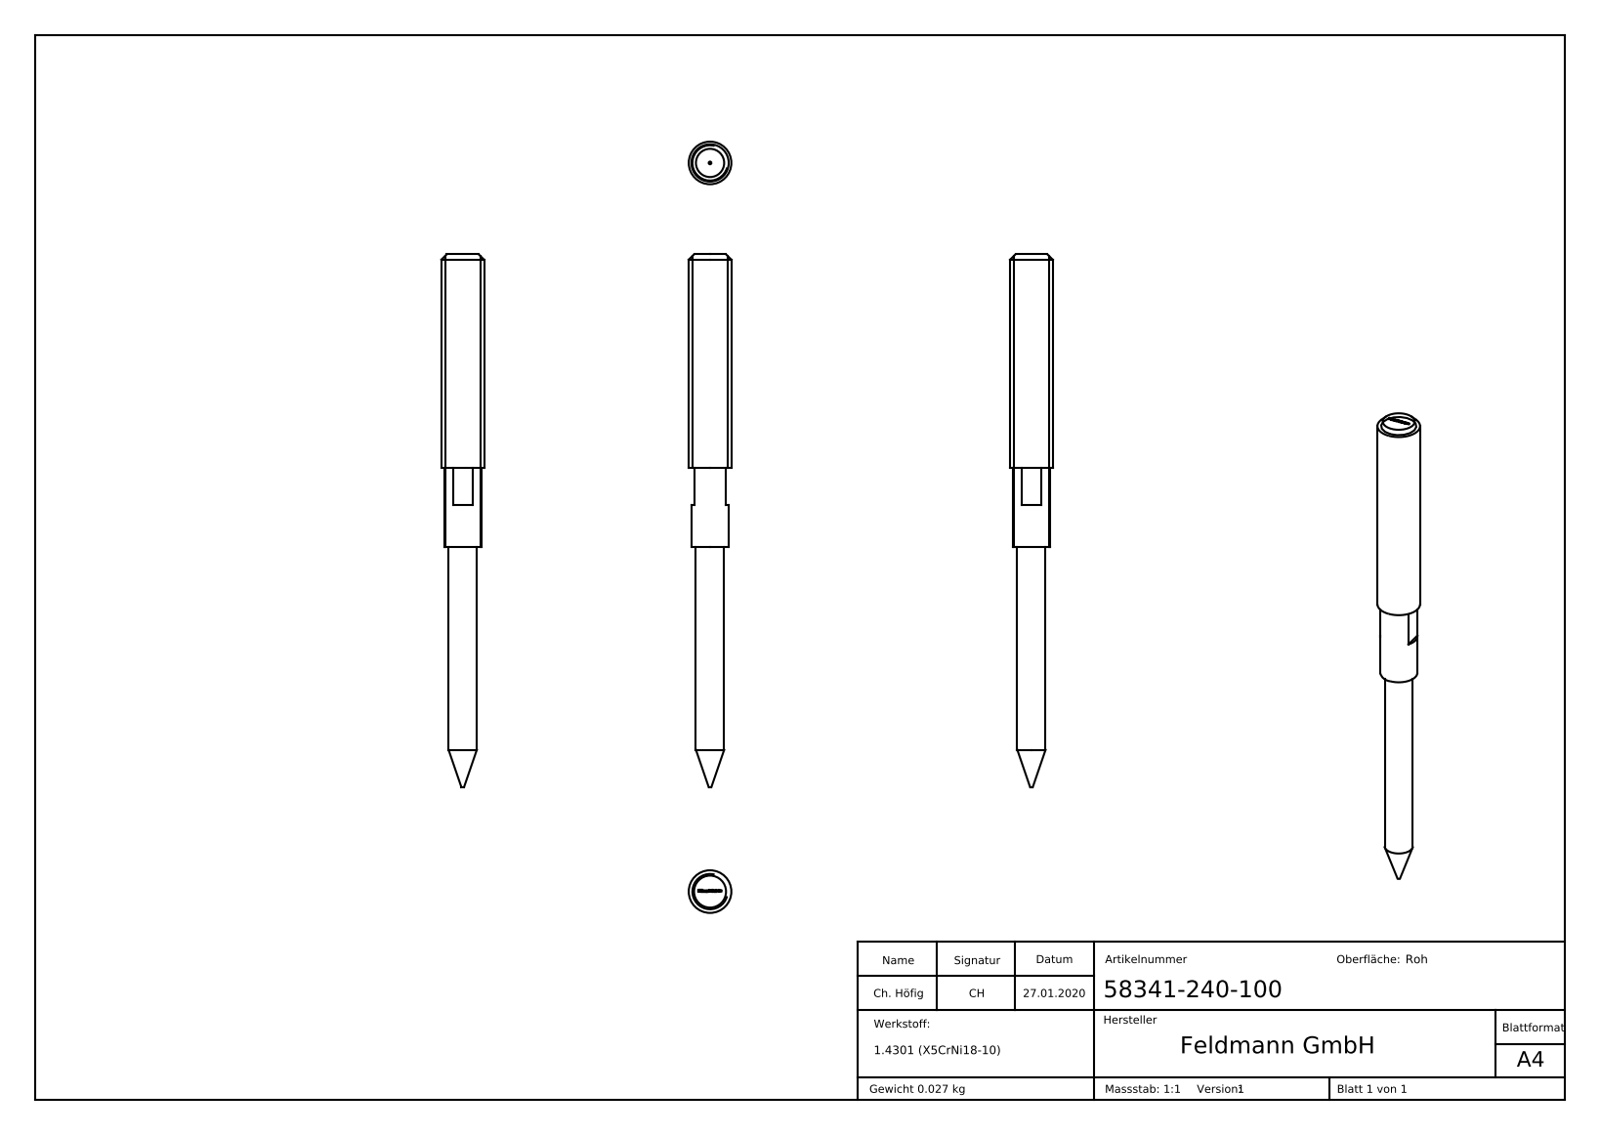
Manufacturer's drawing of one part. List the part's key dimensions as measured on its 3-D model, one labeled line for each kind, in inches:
Part name (STEP PRODUCT): 58341-240-100
STEP written by: SolidWorks 2015 (CONFIG_CONTROL_DESIGN)
Units: inches
Bodies: 1 solid, 269 faces (136 planar, 3 cylindrical, 130 other)
Overall size (bounding box): 3.937 × 0.315 × 0.315
Volume: 0.211 in³ · Surface area: 3.258 in²
Round bosses / shafts (diameter × count): ⌀0.315 ×1, ⌀0.276 ×1, ⌀0.209 ×1
Main face-to-face distances: 0.236, 2.165, 0.591, 1.575, 0.315, 0.276, 1.85, 2.161, 1.846, 1.571
